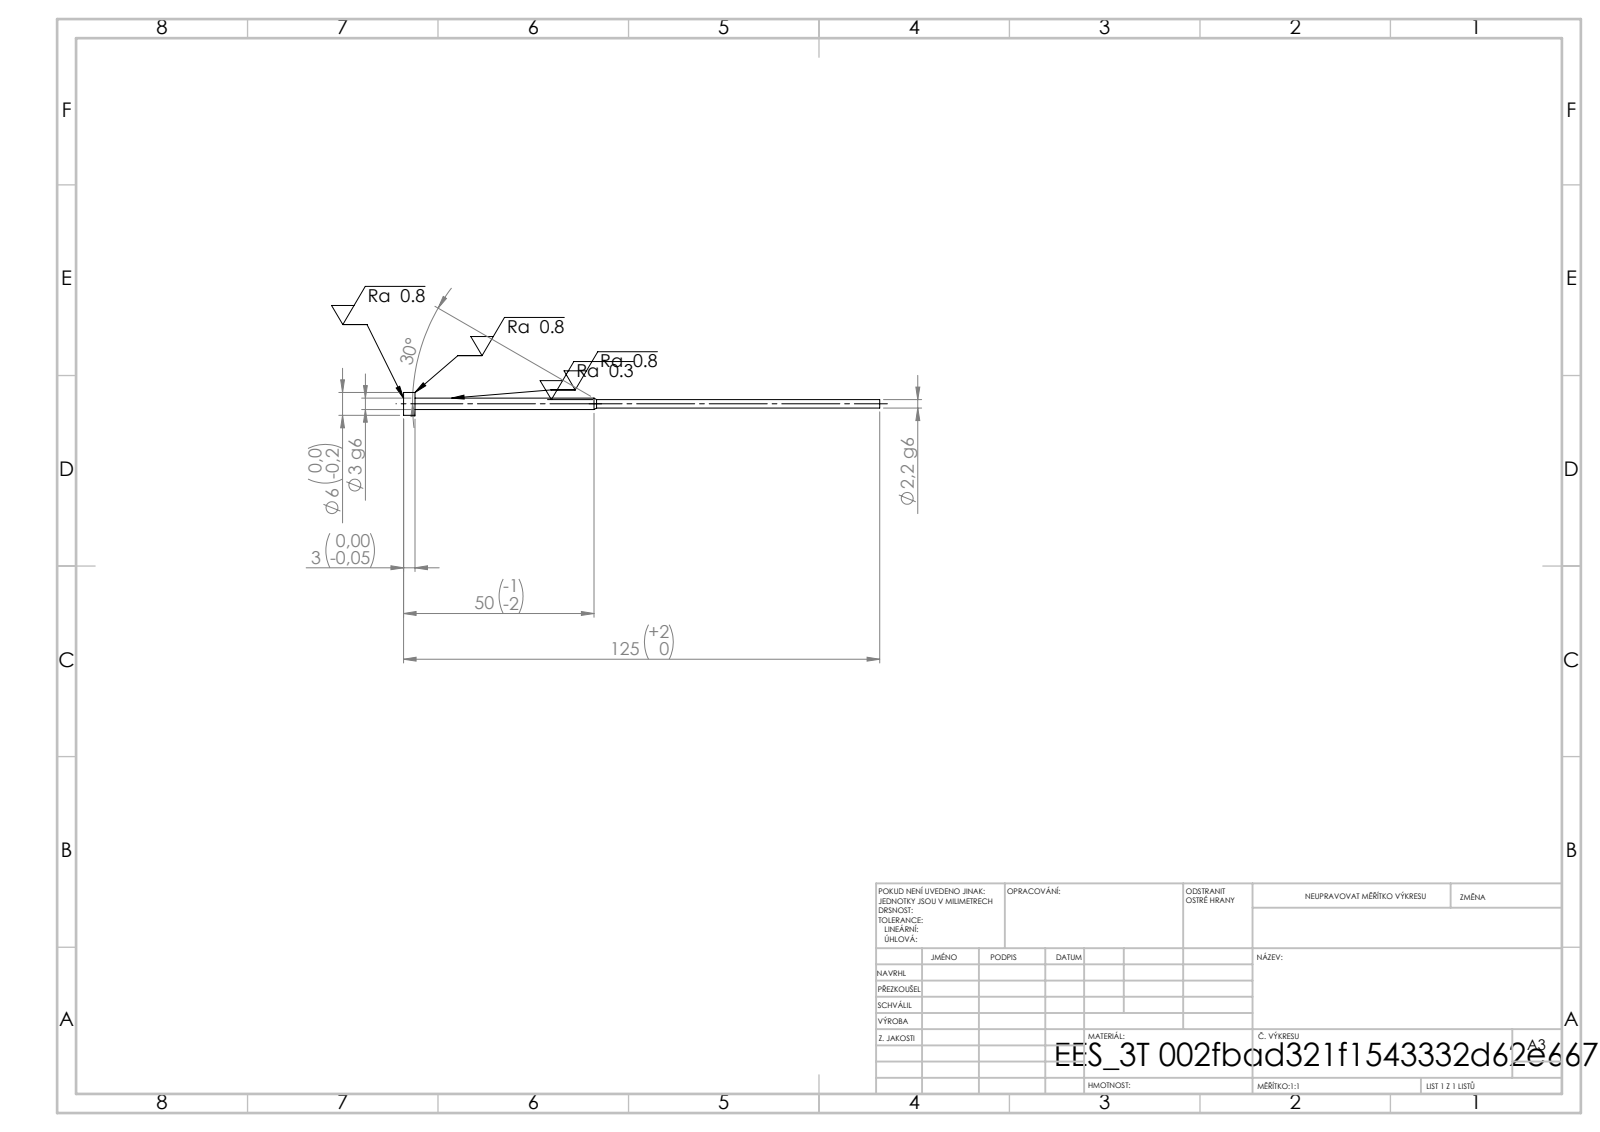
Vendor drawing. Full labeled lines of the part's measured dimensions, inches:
STEP written by: SolidWorks 2019 (CONFIG_CONTROL_DESIGN)
Units: inches
Bodies: 1 solid, 11 faces (3 planar, 6 cylindrical, 2 other)
Overall size (bounding box): 4.921 × 0.236 × 0.236
Volume: 0.043 in³ · Surface area: 1.663 in²
Round bosses / shafts (diameter × count): ⌀0.236 ×1, ⌀0.118 ×1, ⌀0.087 ×1
Main face-to-face distances: 0.118, 4.803, 4.921
